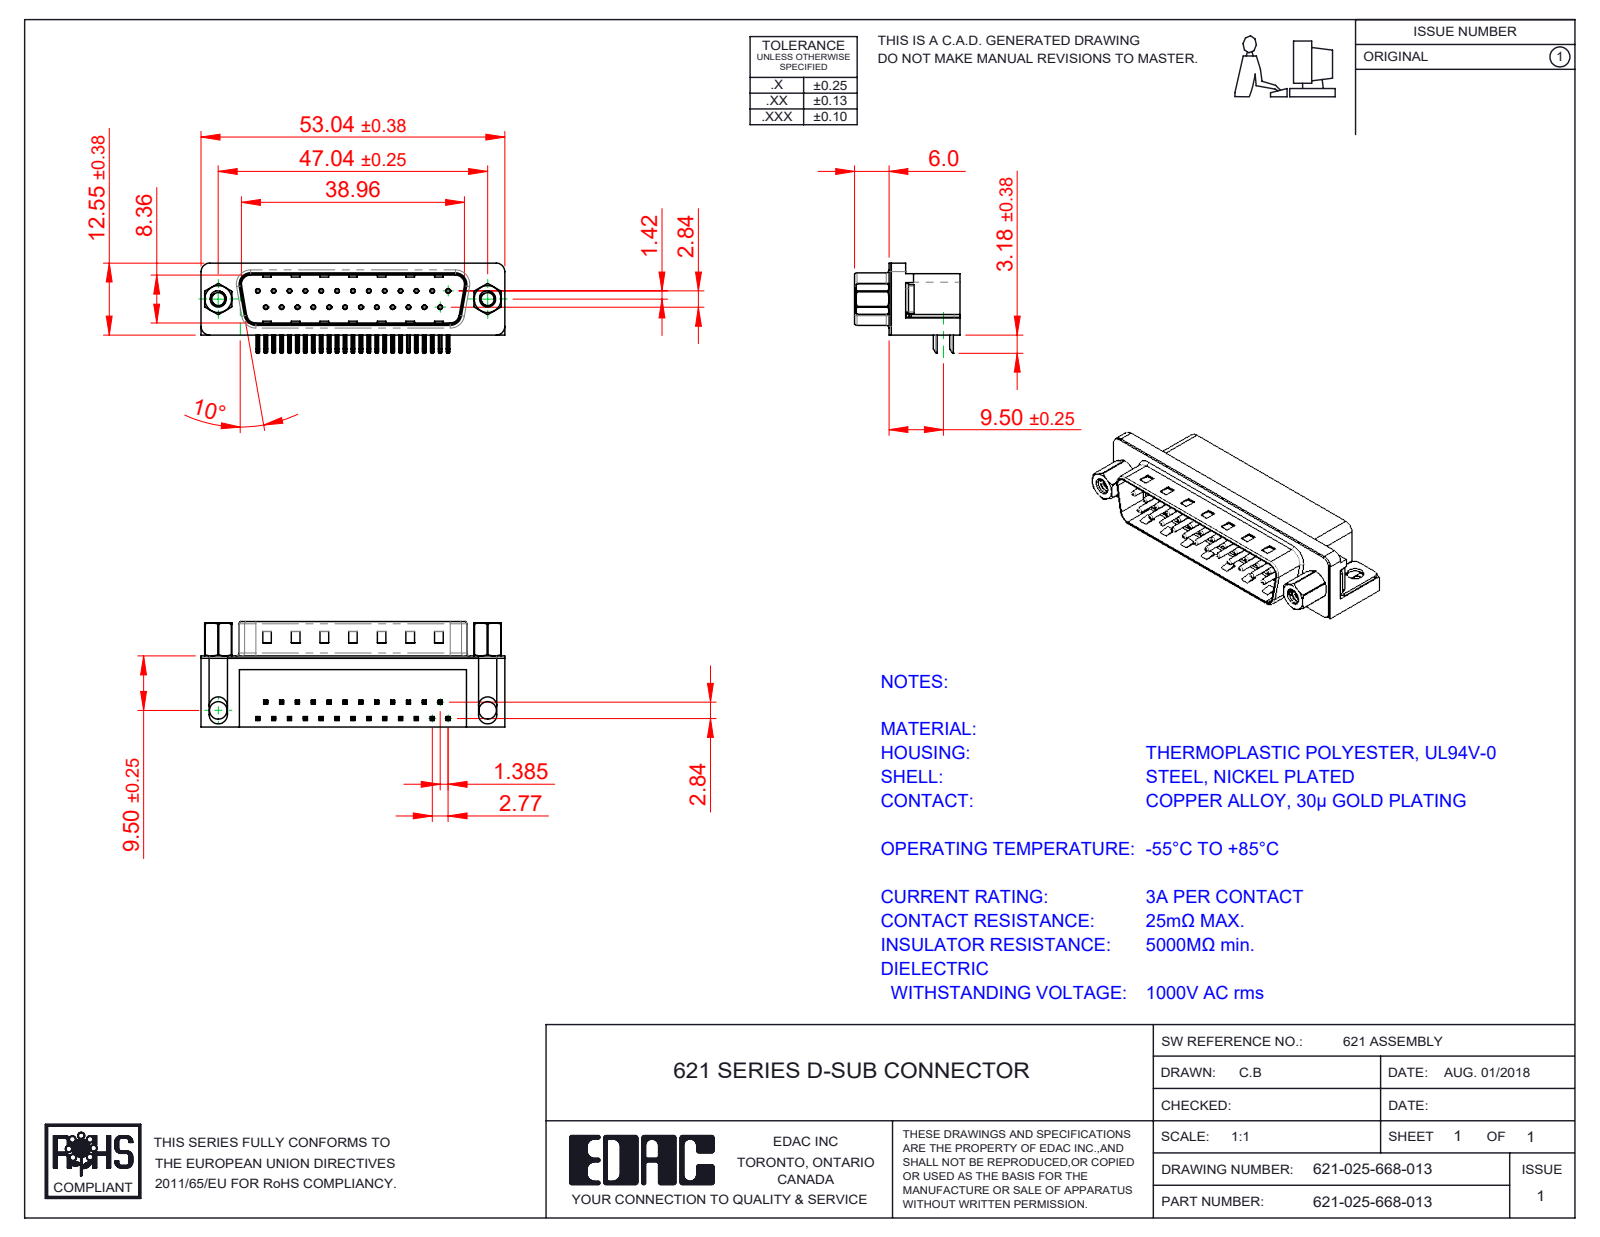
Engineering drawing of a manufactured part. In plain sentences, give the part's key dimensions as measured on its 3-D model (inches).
The part is named "621 Housing_25 Socket; 621 4-40 Threaded Rivet; 621 Contact Bottom; 621 Thru Hole Board Mount (+4 more)". Its 3-D file was written by "SolidWorks 2016 (CONFIG_CONTROL_DESIGN)". It is 33 solids with 2387 faces: 1425 planar, 731 cylindrical and 231 other. Overall it measures 2.088 by 0.724 by 0.619 inches. Its volume is 0.4 cubic inches and its surface area 12.64 square inches. Round holes: 25 of diameter 0.014, 25 of diameter 0.031, 2 of diameter 0.089, 2 of diameter 0.09, 2 of diameter 0.12, 2 of diameter 0.157, 2 of diameter 0.189, 2 of diameter 0.197. Round bosses or shafts: 25 of diameter 0.03, 2 of diameter 0.193, 2 of diameter 0.187, 2 of diameter 0.154, 2 of diameter 0.11. Partial cylindrical surfaces (rounded edges, fillets, slot ends): 108 of radius 0.01, 50 of radius 0.005, 16 of radius 0.039, 9 of radius 0.02, 8 of radius 0.063, 7 of radius 0.059, 4 of radius 0.035, 4 of radius 0.079. The main face-to-face distances are 0.016, 0.472, 0.407, 0.083, 0.345, 0.412, 0.067, 0.428, 0.488, 0.354. The hole center spacings are 0.124, 0.109, 0.218, 0.327, 0.436, 0.545, 0.654, 0.198.
